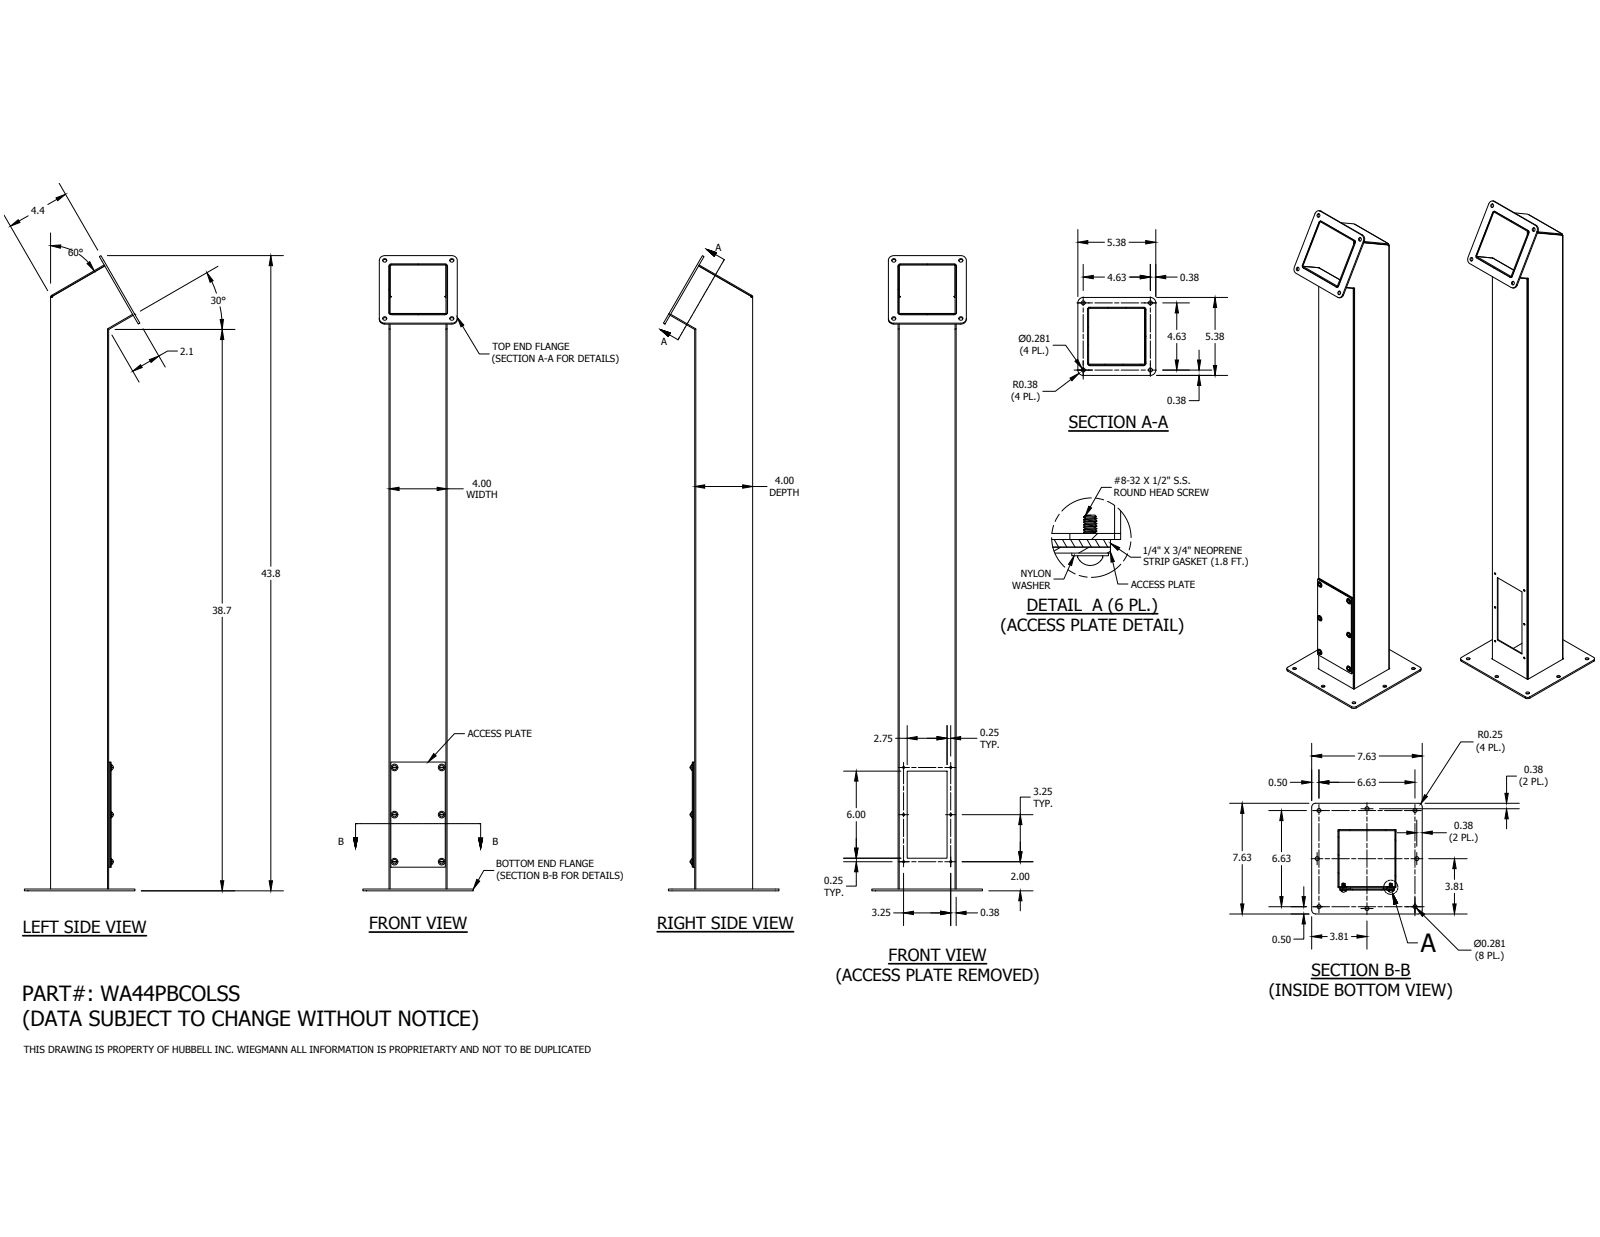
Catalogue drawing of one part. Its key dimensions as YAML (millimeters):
part_name: "WA44PBCOLSSFRONT; WA44PBCOLSSBLR; WA44CCOLSSBASERING; WA44CCOLSSCOVER (+5 more)"
step_written_by: "Autodesk Inventor 2016 (AUTOMOTIVE_DESIGN)"
units: millimeters
bodies: {solids: 24, faces: 358, planar: 214, cylindrical: 104, other: 40}
overall_size: [1111.95, 202.37, 193.68]
volume: 955752
surface_area: 988313
round_holes:
  - {diameter: 7.14, count: 12}
  - {diameter: 3.56, count: 6}
  - {diameter: 6.35, count: 6}
  - {diameter: 7.06, count: 6}
round_bosses_or_shafts:
  - {diameter: 11.51, count: 6}
  - {diameter: 7.85, count: 6}
  - {diameter: 4.17, count: 6}
  - {diameter: 3.13, count: 6}
partial_cylinders:
  - {radius: 2.27, count: 6}
  - {radius: 1.78, count: 5}
  - {radius: 0.79, count: 4}
  - {radius: 2.67, count: 4}
  - {radius: 4.76, count: 4}
  - {radius: 6.35, count: 4}
  - {radius: 9.53, count: 4}
face_to_face_distances: [1.88, 99.72, 97.84, 101.6, 103.98, 4.26, 3.17, 102.1, 2.38, 105.86]
hole_center_spacings: [82.55, 84.2, 116.74, 190.98, 165.1, 123.47, 168.28, 82.54]
